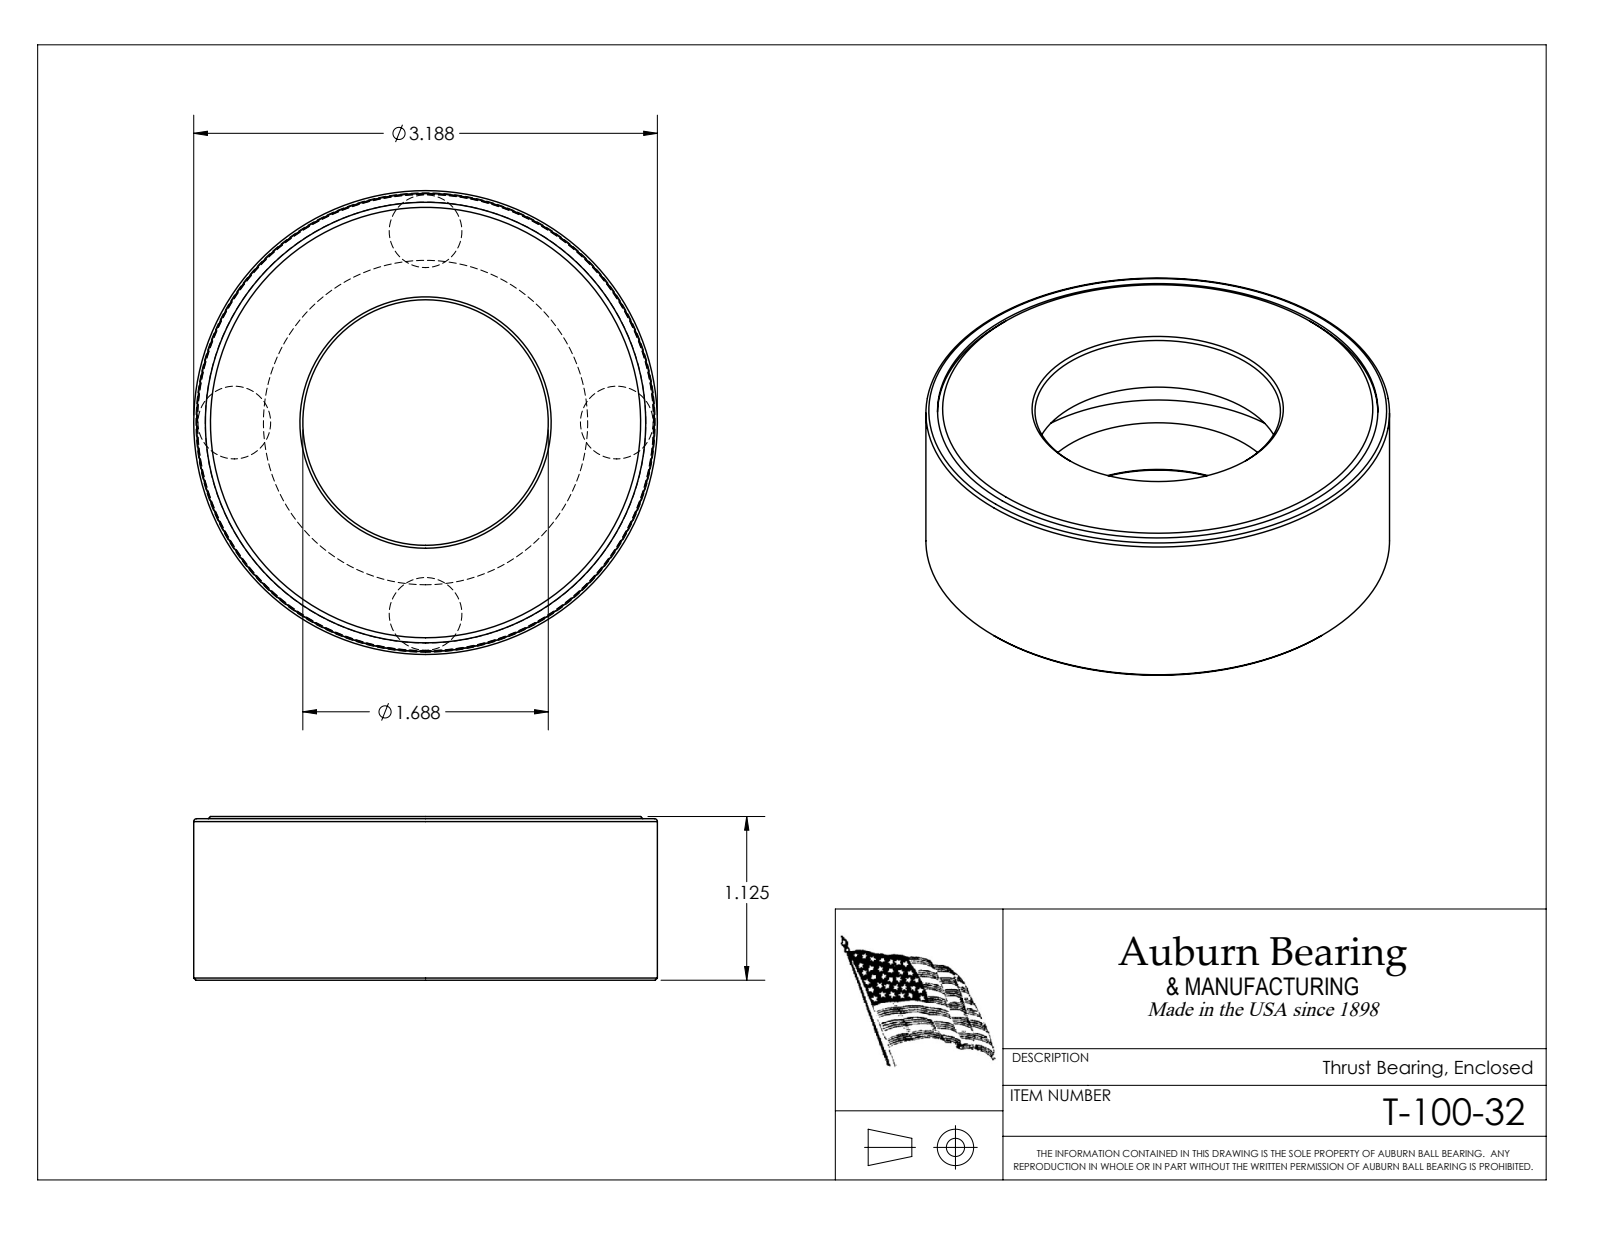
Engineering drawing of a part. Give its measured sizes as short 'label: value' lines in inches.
name: T-100-32
written by: SolidWorks 2016 (CONFIG_CONTROL_DESIGN)
unit: in
bodies: 6 solids, 28 faces (9 planar, 7 cylindrical, 12 other)
size: 3.188 × 3.188 × 1.125
volume: 4.536 in³; area: 53.49 in²
holes: 1× ⌀1.687, 1× ⌀3.027, 1× ⌀3.147
bosses: 1× ⌀3.187, 1× ⌀3.133
face distances: 1.125, 0.413, 0.712, 0.713, 0.3, 0.412, 1.09, 0.678, 0.378, 0.035
